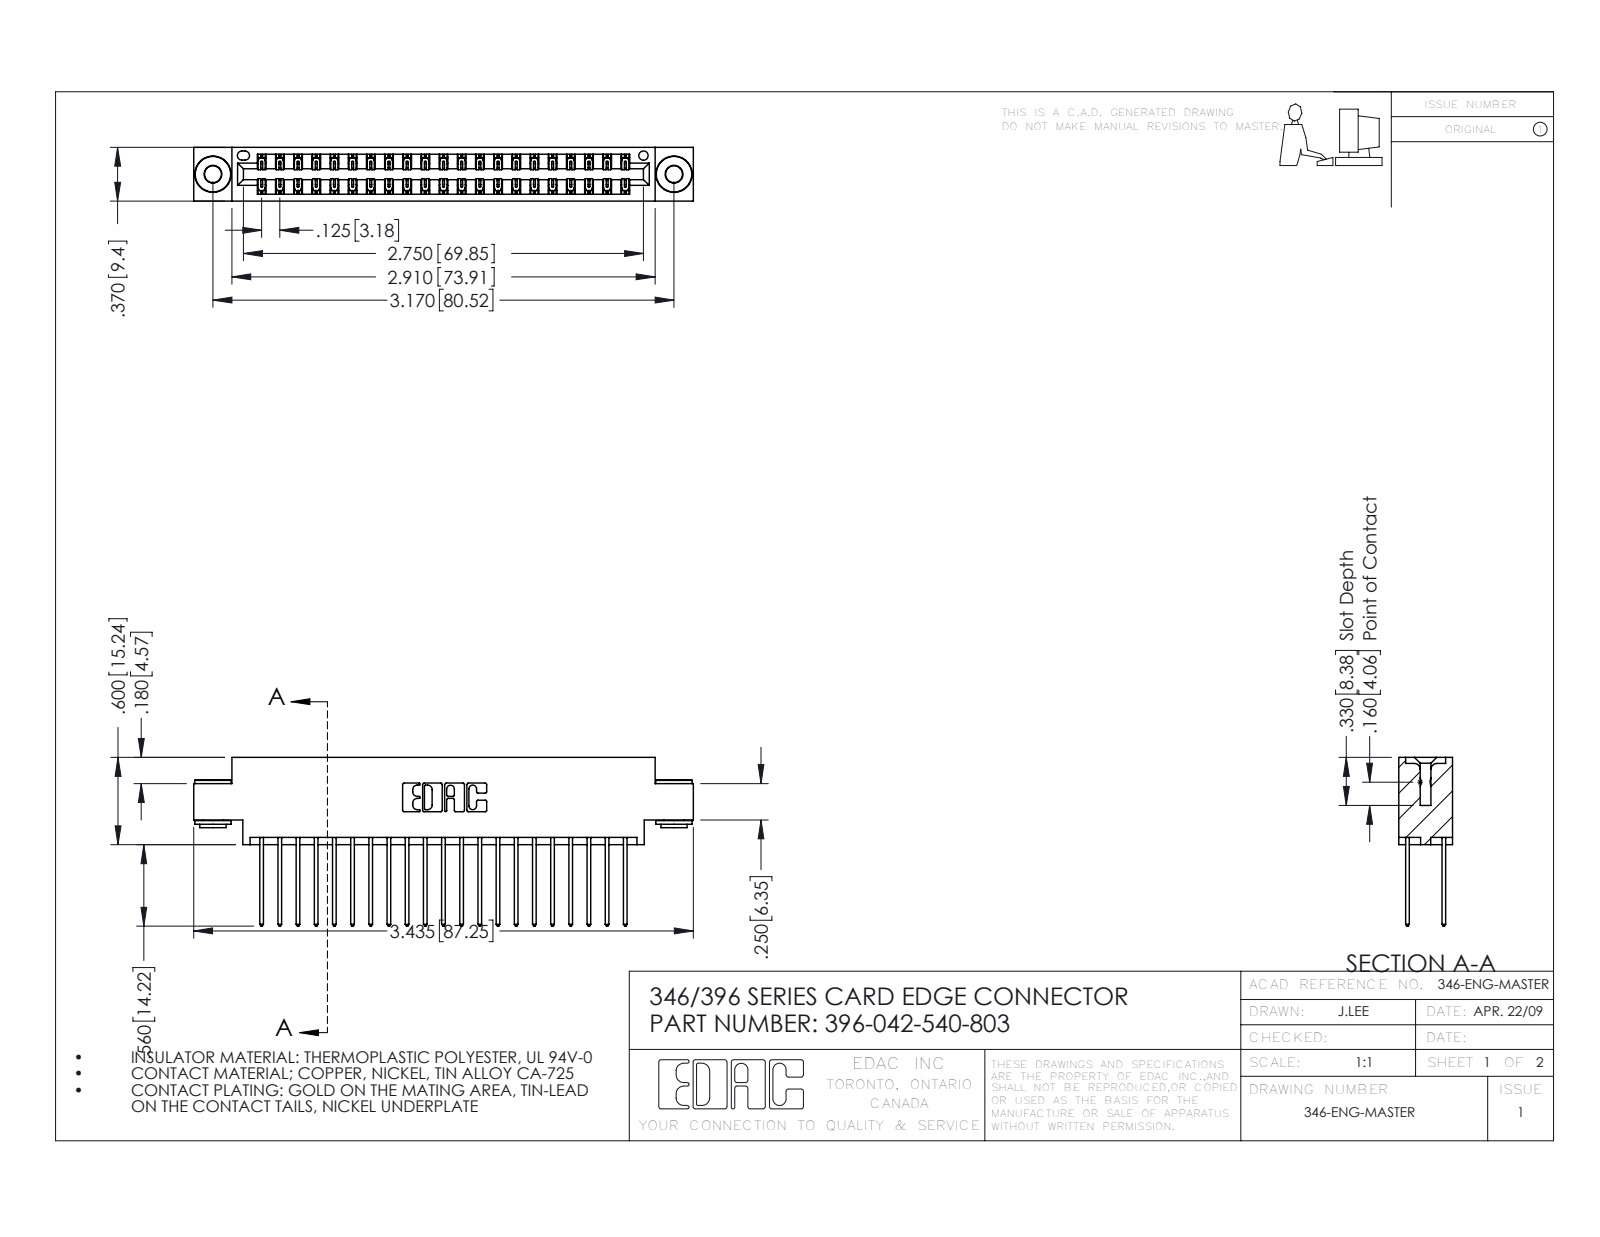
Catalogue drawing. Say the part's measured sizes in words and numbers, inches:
The part is named "396-042-540-803; 345-292-001_345-293-140; 345-250-002_345-250-002-102; 346 Part_0.170 Offset - 0.156 Dia-TH". Its 3-D file was written by "SolidWorks 2016 (CONFIG_CONTROL_DESIGN)". It is 45 solids with 2348 faces: 1560 planar, 780 cylindrical and 8 other. Overall it measures 3.435 by 1.16 by 0.37 inches. Its volume is 0.511 cubic inches and its surface area 19.1 square inches. Round holes: 2 of diameter 0.116, 2 of diameter 0.156, 1 of diameter 0.064. Round bosses or shafts: 2 of diameter 0.25, 2 of diameter 0.18, 2 of diameter 0.136. Partial cylindrical surfaces (rounded edges, fillets, slot ends): 63 of radius 0.006, 42 of radius 0.01, 22 of radius 0.01, 6 of radius 0.007, 6 of radius 0.031, 3 of radius 0.026, 2 of radius 0.014, 2 of radius 0.022. The main face-to-face distances are 0.048, 0.322, 0.25, 0.37, 0.025, 0.072, 0.298, 0.275, 0.148, 0.222. The hole center spacings are 0.246, 2.963, 3.17.
